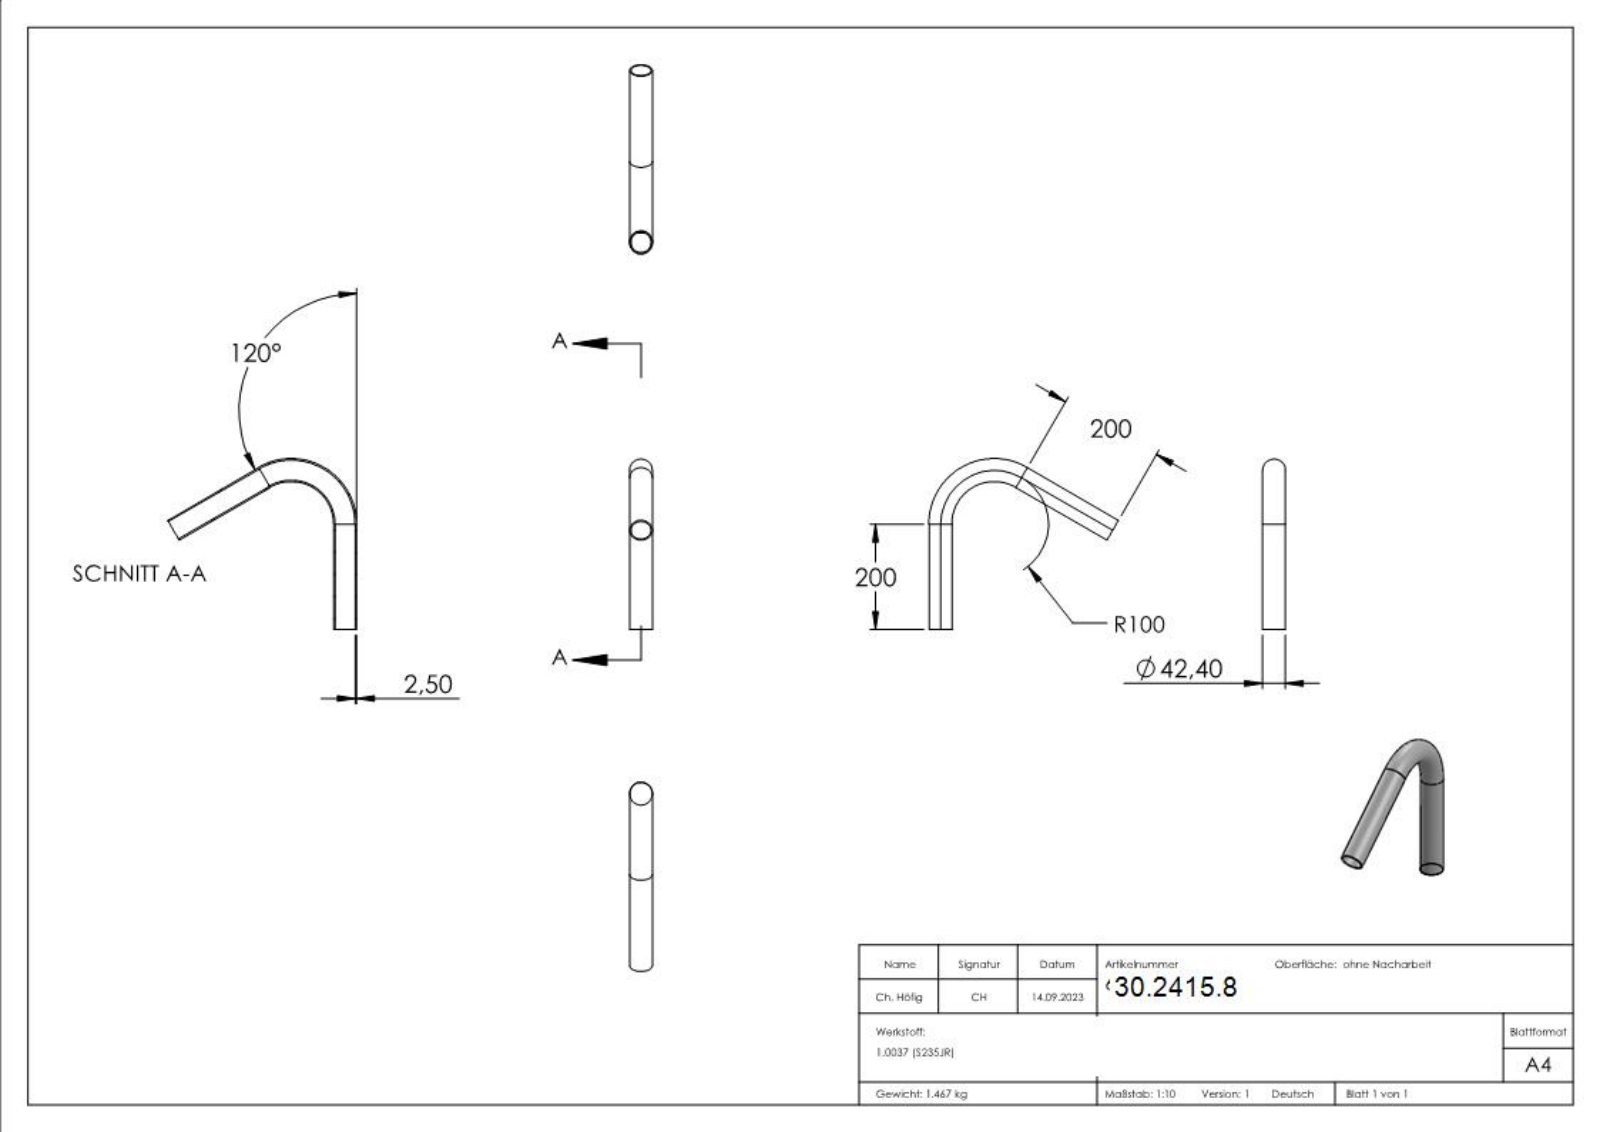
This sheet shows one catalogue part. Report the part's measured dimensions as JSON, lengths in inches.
{"part_name": "6967-120", "step_written_by": "SolidWorks 2018 (CONFIG_CONTROL_DESIGN)", "units": "inches", "bodies": {"solids": 1, "faces": 206, "planar": 110, "cylindrical": 4, "other": 92}, "overall_size": [13.816, 12.46, 1.669], "volume_in3": 11.47, "surface_area_in2": 234.1, "round_holes": [[1.472, 2]], "round_bosses_or_shafts": [[1.669, 2]], "face_to_face_distances": [0.021, 0.019, 0.013, 0.021, 0.012, 0.023, 0.015, 0.019, 0.013, 0.014]}
